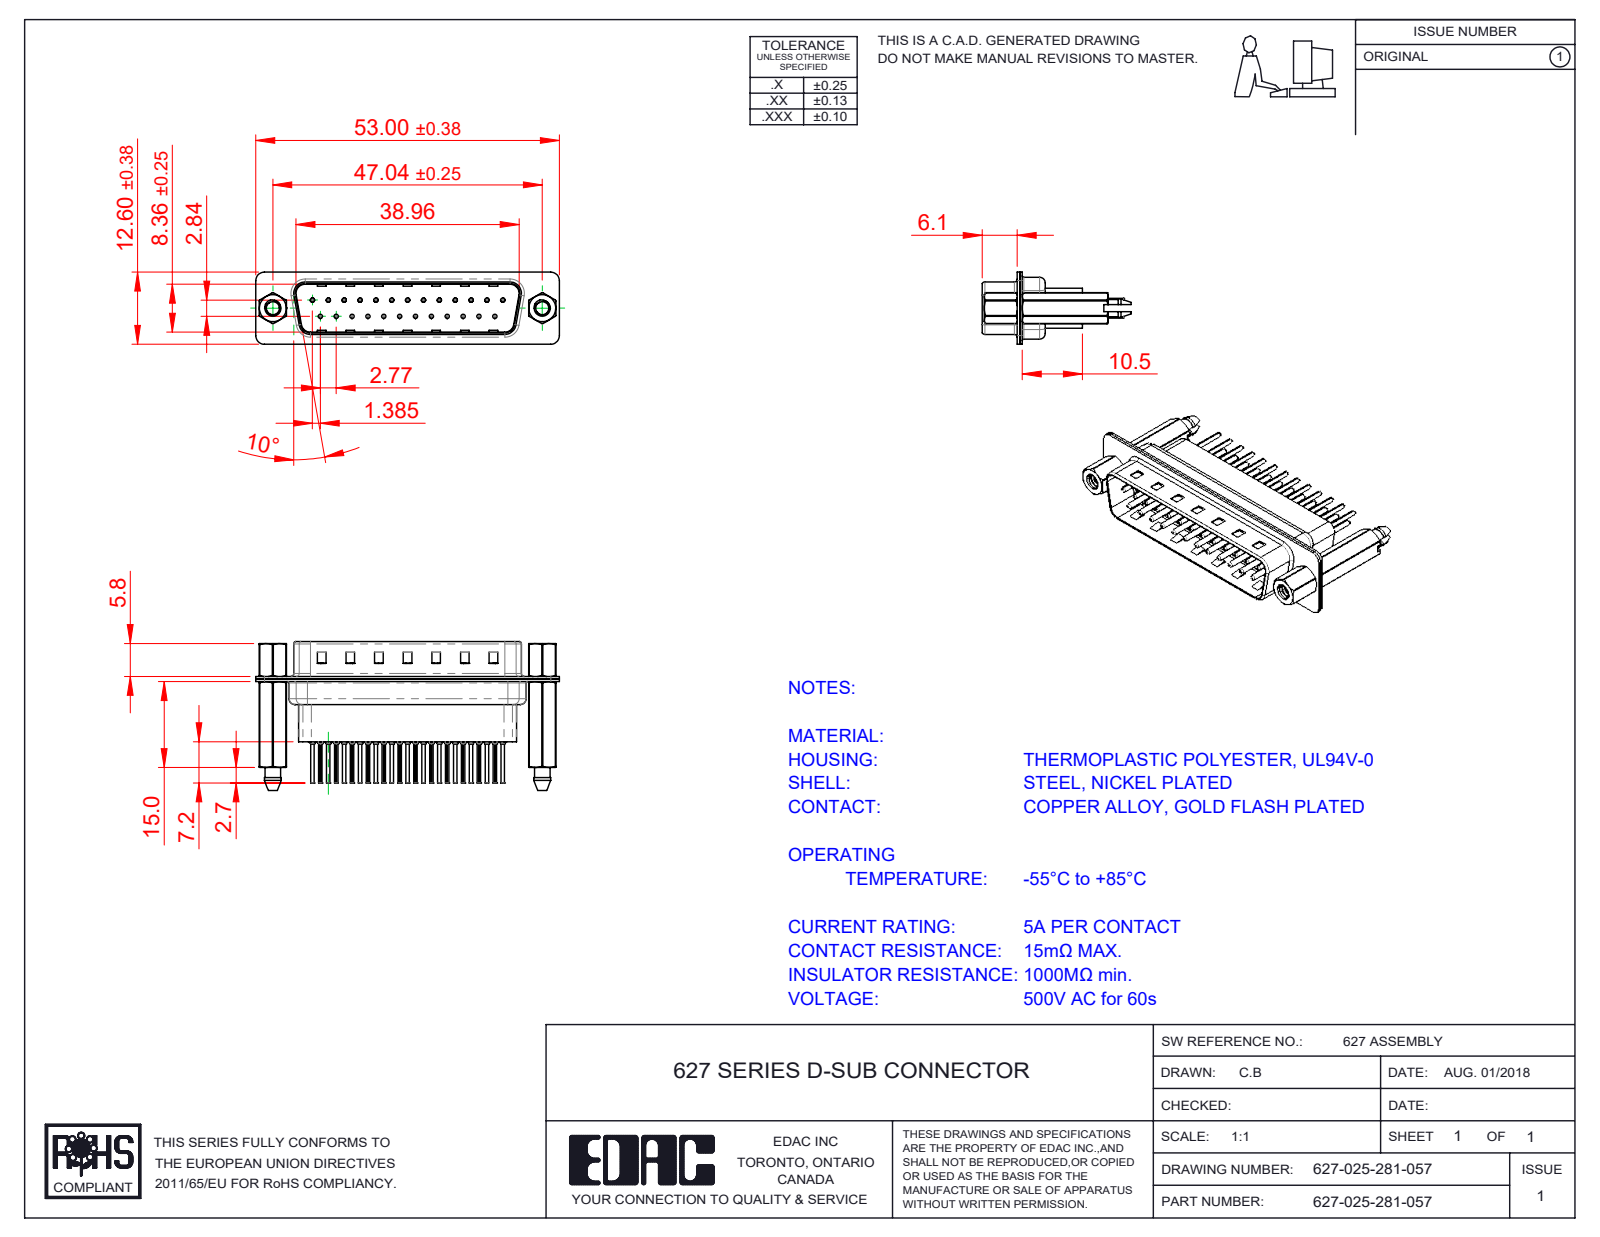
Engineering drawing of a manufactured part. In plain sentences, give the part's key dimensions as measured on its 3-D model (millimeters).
The part is named "627 Shell Rear_25 Contacts; 627 Housing_25 HP; 627 4-40 Threaded Boardlock_HP81; 627 Shell Front_25 Contacts (+4 more)". Its 3-D file was written by "SolidWorks 2020 (CONFIG_CONTROL_DESIGN)". It is 32 solids with 3060 faces: 825 planar, 1200 cylindrical and 1035 other. Overall it measures 53 by 25.9 by 12.6 millimeters. Its volume is 4 417 cubic millimeters and its surface area 11 314 square millimeters. Round holes: 25 of diameter 0.2, 25 of diameter 0.35, 25 of diameter 1.1, 25 of diameter 1.6, 2 of diameter 2.26, 2 of diameter 2.29, 2 of diameter 4, 2 of diameter 4.8. Round bosses or shafts: 25 of diameter 2, 25 of diameter 1.5, 25 of diameter 0.75, 25 of diameter 0.6, 2 of diameter 4.9, 2 of diameter 2.79. Partial cylindrical surfaces (rounded edges, fillets, slot ends): 50 of radius 0.1, 18 of radius 1.5, 12 of radius 2, 10 of radius 1.6, 8 of radius 0.5, 4 of radius 0.25, 4 of radius 0.6, 4 of radius 0.65. The main face-to-face distances are 0.4, 0.45, 0.82, 9.58, 0.68, 7.68, 1.5, 0.9, 1.08, 8.08. The hole center spacings are 3.16, 8.31, 2.77, 5.54, 11.08, 16.62, 5.03, 5.04.
